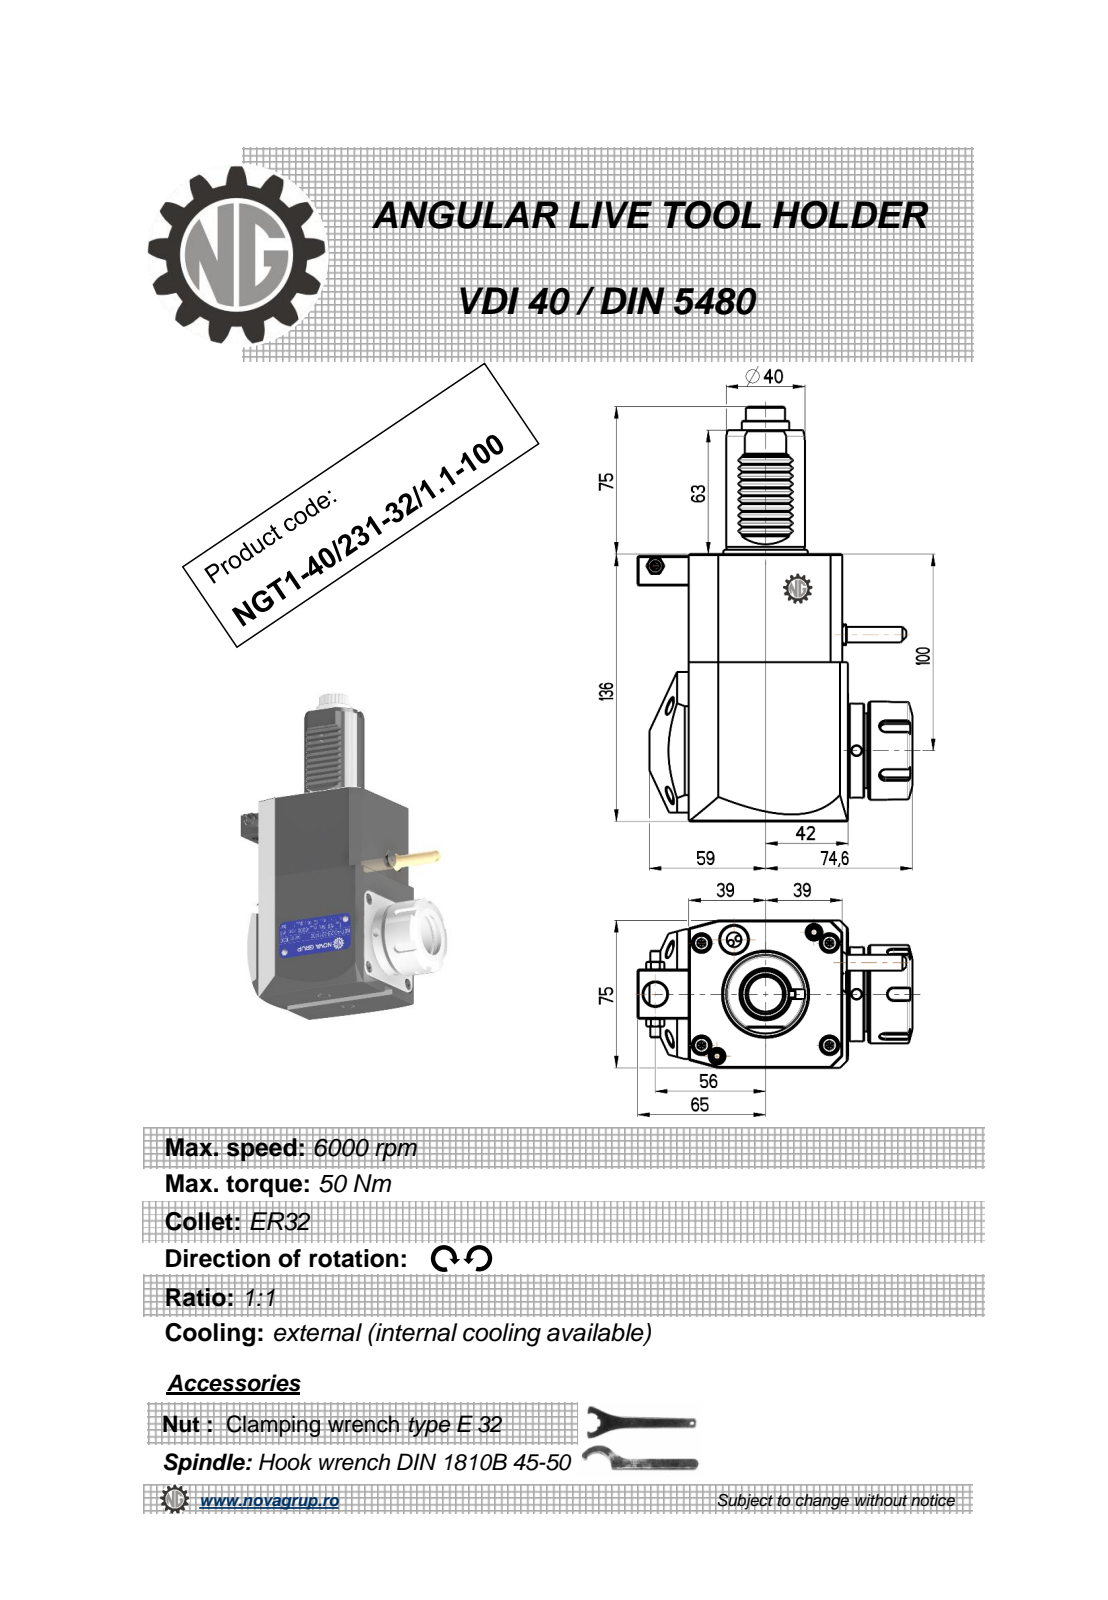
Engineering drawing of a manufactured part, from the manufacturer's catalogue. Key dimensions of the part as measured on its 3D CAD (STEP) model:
Part name (STEP PRODUCT): NGT1_40_231_32_1_1_100
STEP written by: PRO/ENGINEER BY PARAMETRIC TECHNOLOGY CORPORATION, 2010280 (CONFIG_CONTROL_DESIGN)
Units: millimetres
Bodies: 1 solid, 532 faces (193 planar, 185 cylindrical, 154 other)
Overall size (bounding box): 211 × 139.6 × 76.6
Volume: 996 617 mm³ · Surface area: 76 309 mm²
Round holes (diameter × count): ⌀5 ×3, ⌀3 ×1, ⌀4.2 ×1, ⌀9.5 ×1, ⌀12 ×1, ⌀27 ×1
Round bosses / shafts (diameter × count): ⌀50 ×1, ⌀48 ×1, ⌀41 ×1, ⌀40 ×1, ⌀24 ×1, ⌀11.2 ×1, ⌀8.96 ×1, ⌀8 ×1
Partial cylindrical surfaces — rounded edges, fillets, slot ends (radius × count): R2.08 ×48, R0.26 ×12, R0.3 ×10, R0.22 ×6, R3 ×5, R9.08 ×1, R9.92 ×1, R15 ×1
Main face-to-face distances: 75, 136, 78, 81, 3, 80.8, 2.8, 4.5, 7.5, 0.5
Hole centre spacings: 36.22, 61.13, 91.5, 102.25, 138.89
